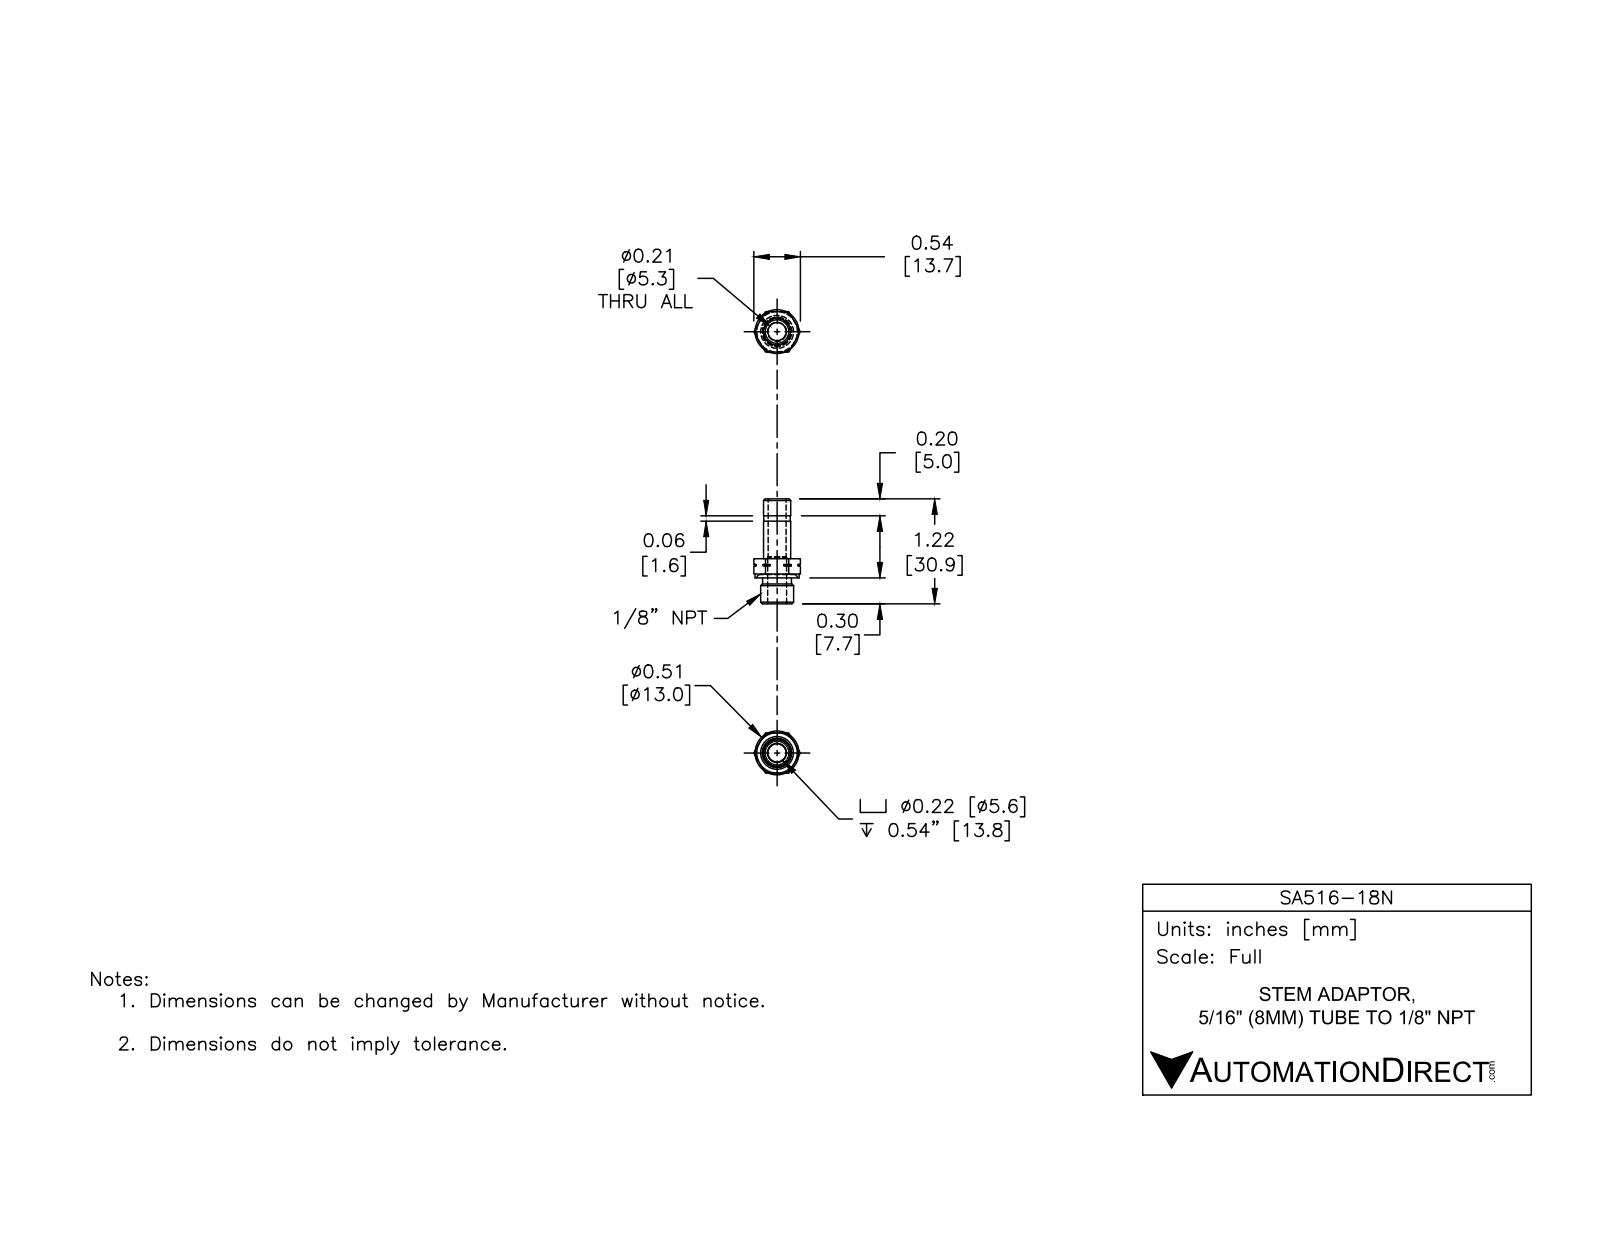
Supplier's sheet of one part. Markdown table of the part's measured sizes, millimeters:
| quantity | value |
| --- | --- |
| part name | SA516-18N |
| STEP written by | SolidWorks 2015 (CONFIG_CONTROL_DESIGN) |
| units | millimeters |
| bodies | 2 solids, 74 faces (25 planar, 23 cylindrical, 26 other) |
| overall size | 30.93 × 13.74 × 13 |
| volume | 1 489 mm³ |
| surface area | 1 869 mm² |
| round holes (diameter × count) | 5.3 × 1, 5.6 × 1 |
| round bosses / shafts (diameter × count) | 13 × 1, 9.7 × 1, 8.5 × 1, 8 × 1, 7.75 × 1 |
| partial cylindrical surfaces (radius × count) | 6.29 × 1 |
| main face-to-face distances | 11.9, 5.65, 7.65, 13.3, 30.92, 23.27, 17.62, 8.8, 1.15, 4.5 |
